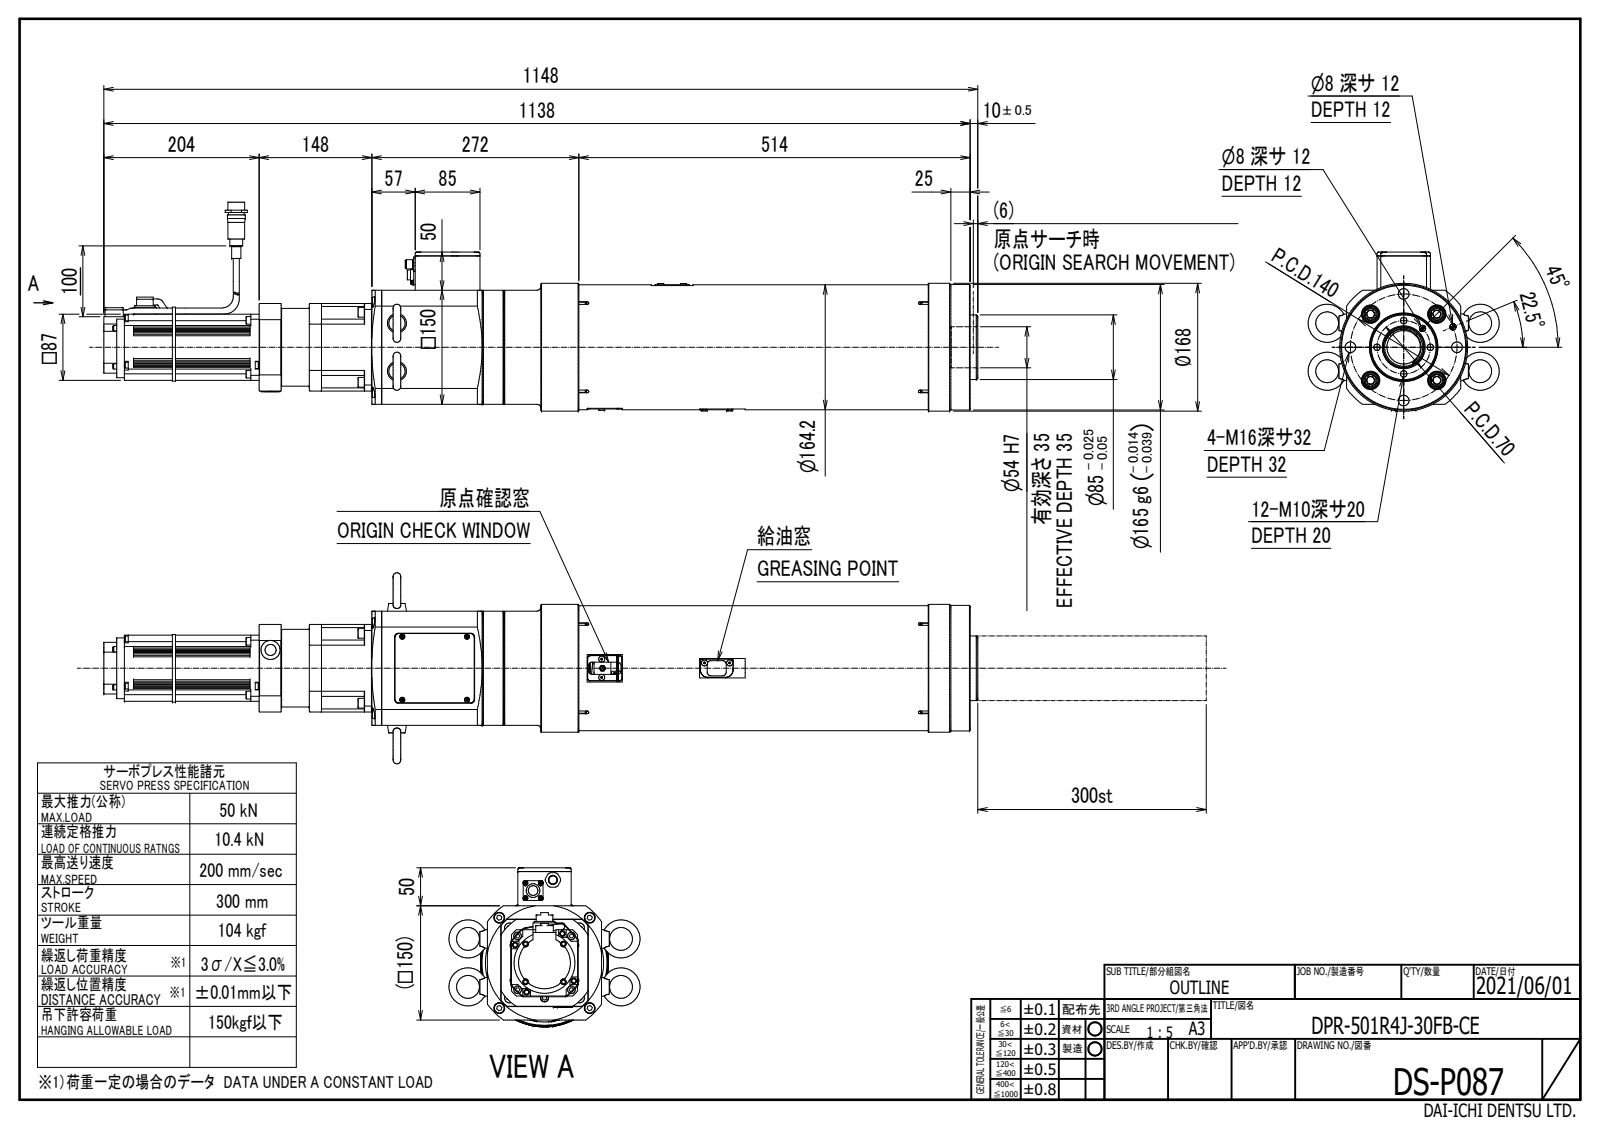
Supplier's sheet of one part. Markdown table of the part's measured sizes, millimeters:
| quantity | value |
| --- | --- |
| part name | DPR-501R4J-30FB-CE(DS-P087) |
| STEP written by | Autodesk Inventor 2021 (AUTOMOTIVE_DESIGN) |
| units | millimeters |
| bodies | 1 solid, 1781 faces (1035 planar, 449 cylindrical, 297 other) |
| overall size | 1148 × 251 × 209 |
| volume | 19 600 000 mm³ |
| surface area | 761 038 mm² |
| round holes (diameter × count) | 14 × 8, 8 × 6, 10.5 × 6, 2.46 × 4, 3.1 × 4, 3.2 × 4, 3.4 × 4, 8.5 × 4, 10.25 × 4, 11 × 4, 24 × 4, 5 × 1 |
| round bosses / shafts (diameter × count) | 10 × 14, 8 × 12, 13 × 8, 6 × 8, 22 × 4, 8.5 × 4, 7.5 × 4, 7 × 4 |
| partial cylindrical surfaces (radius × count) | 0.6 × 48, 5 × 37, 1 × 36, 2 × 18, 3 × 12, 2.5 × 8, 0.5 × 7, 1.5 × 7 |
| main face-to-face distances | 101, 14, 31.5, 17.5, 132.5, 118.5, 150, 1.5, 46.5, 29 |
| hole center spacings | 50.93, 35, 44.31, 60.34, 64.22, 78.26, 89.73, 104.11 |
